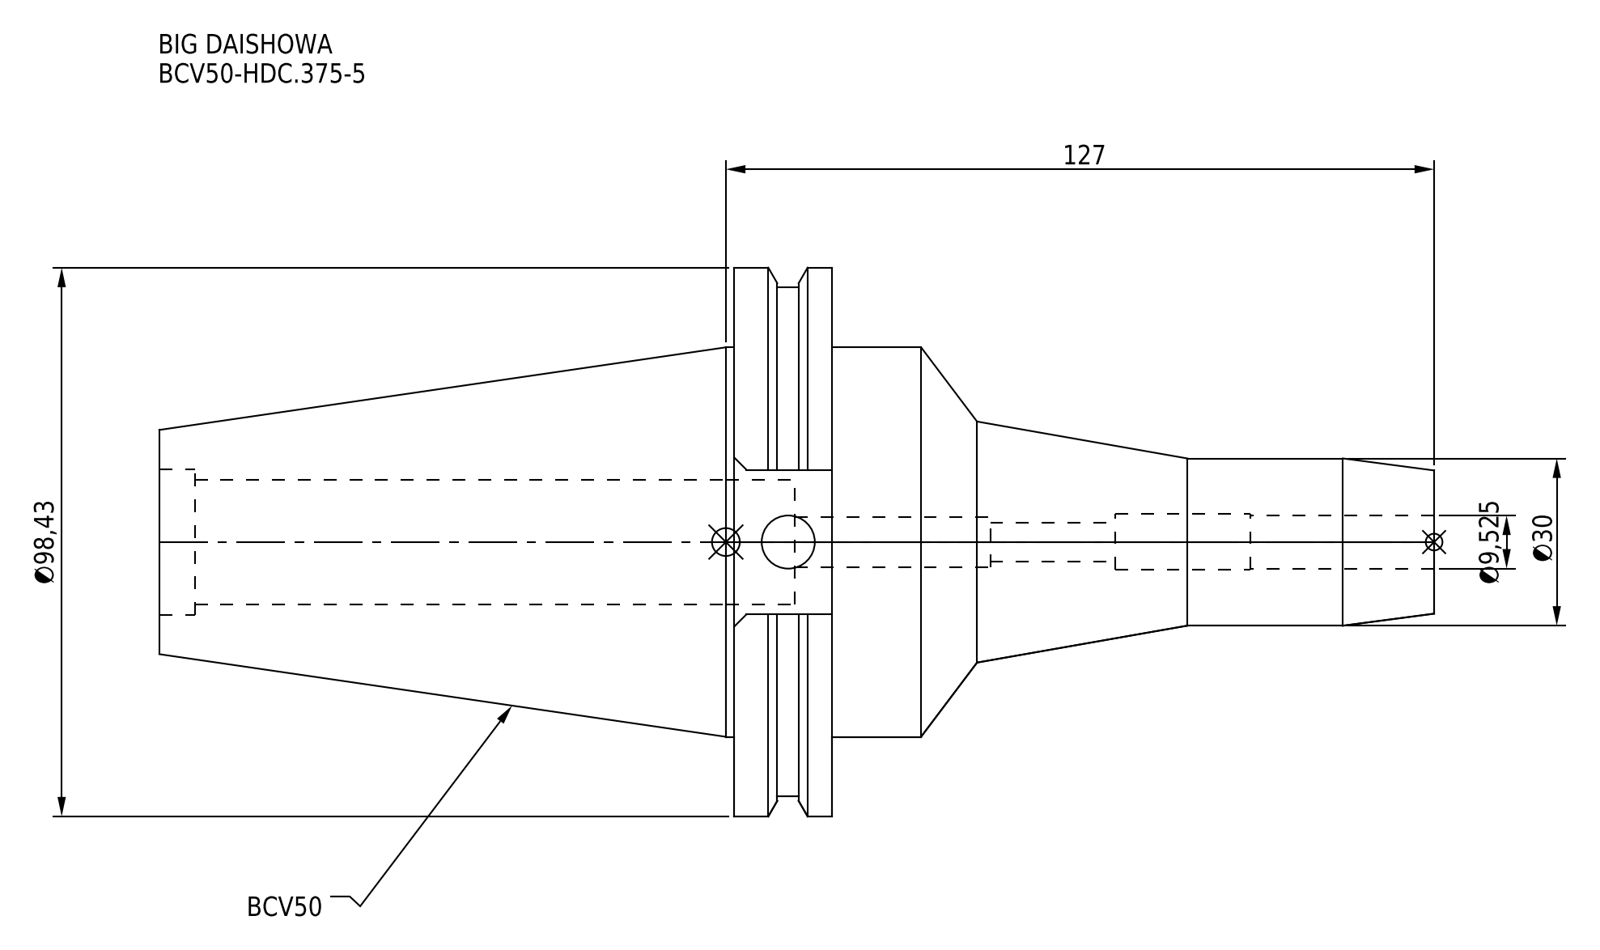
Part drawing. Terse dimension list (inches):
name: BCV50-HDC_375-5
written by: CREO PARAMETRIC BY PTC INC, 2016380 (AUTOMOTIVE_DESIGN)
unit: in
bodies: 1 solid, 64 faces (24 planar, 28 cylindrical, 12 other)
size: 9 × 3.875 × 3.738
volume: 28.98 in³; area: 92.15 in²
holes: 2× ⌀0.375, 1× ⌀0.276, 1× ⌀0.354, 1× ⌀0.394, 1× ⌀0.878, 1× ⌀1.033
bosses: 1× ⌀3.875, 1× ⌀3.594, 1× ⌀2.75, 1× ⌀1.181
face distances: 0.691, 4.75, 4.059, 4.25, 4.941, 9, 2.872, 4.512, 0.262, 0.429
